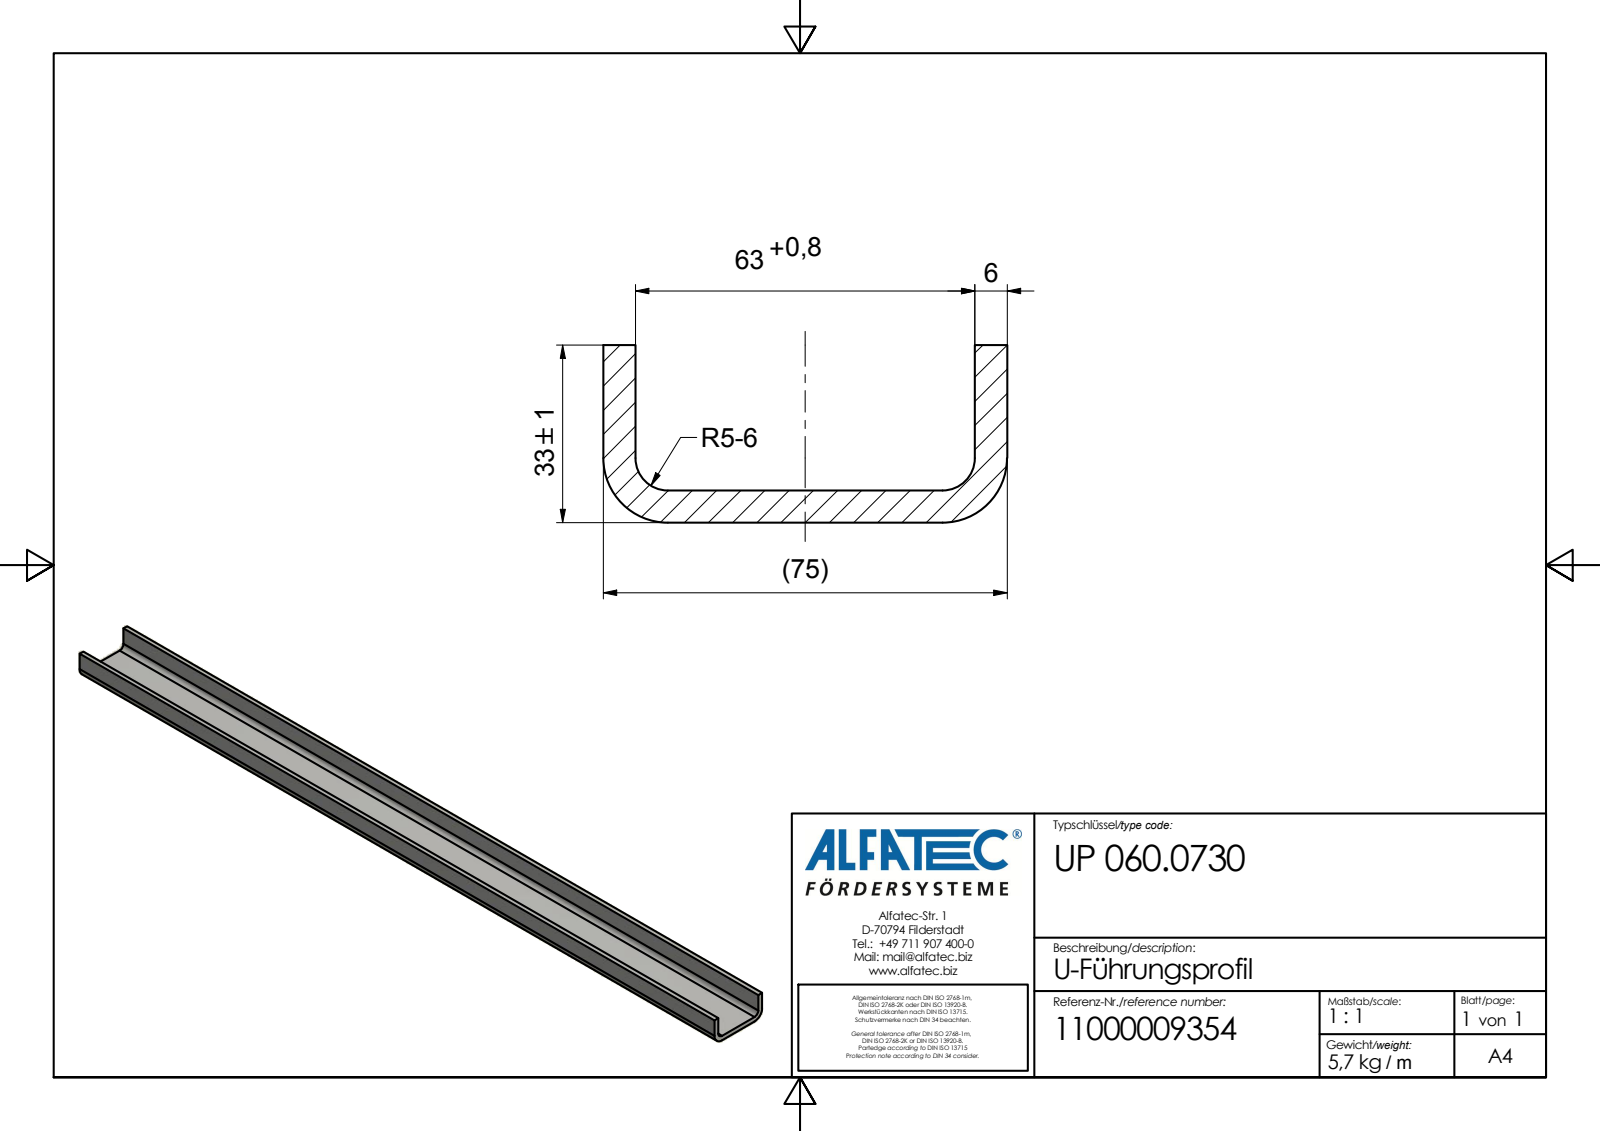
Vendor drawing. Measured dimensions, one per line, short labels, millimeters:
name: UP 060.0730
written by: Autodesk Inventor 2020 (AUTOMOTIVE_DESIGN)
unit: mm
bodies: 1 solid, 14 faces (10 planar, 4 cylindrical, 0 other)
size: 1000 × 75 × 33
volume: 727 646 mm³; area: 256 004 mm²
rounds: 2× R6, 2× R12
face distances: 6, 69, 63, 75, 33, 27, 1000
